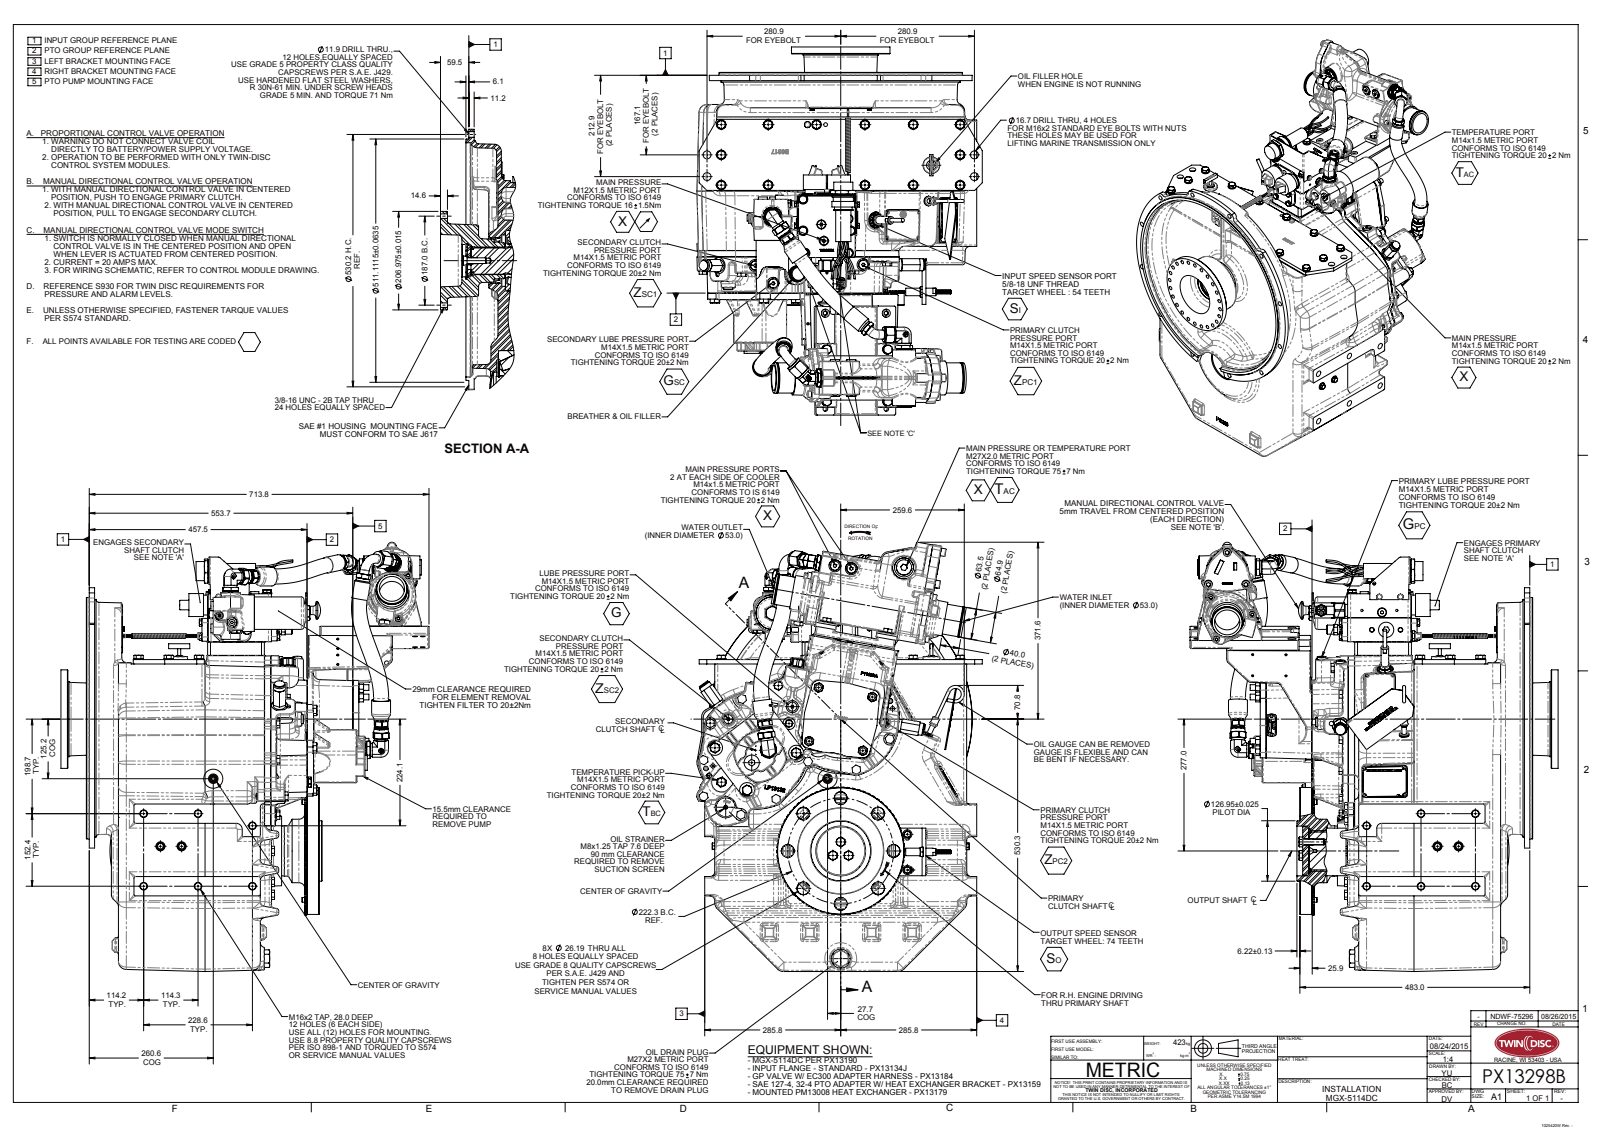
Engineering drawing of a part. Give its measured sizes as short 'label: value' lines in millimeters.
name: PX13298B
written by: SolidWorks 2010 (AUTOMOTIVE_DESIGN)
unit: mm
bodies: 0 solids, 6691 faces (2223 planar, 2403 cylindrical, 2065 other)
size: 901.9 × 773.34 × 599.59
holes: 26× ⌀9.52, 12× ⌀11.9, 8× ⌀26.19, 6× ⌀10, 6× ⌀16, 5× ⌀4.2, 5× ⌀25, 4× ⌀8.8, 4× ⌀16.67, 3× ⌀40, 2× ⌀3, 2× ⌀4.8
bosses: 19× ⌀19.85, 14× ⌀19, 9× ⌀13, 7× ⌀19.05, 6× ⌀20, 5× ⌀12, 4× ⌀33.96, 4× ⌀32
rounds: 132× R20.14, 94× R2, 77× R1.5, 73× R5, 72× R10, 68× R45.92, 66× R1.27, 66× R4
face distances: 320.23, 9.27, 22.03, 298.2, 8.5, 13.53, 306.7, 0.42, 13.11, 21.61
hole spacings: 265.09, 137.24, 265.11, 374.92, 459.18, 512.13, 16, 76
